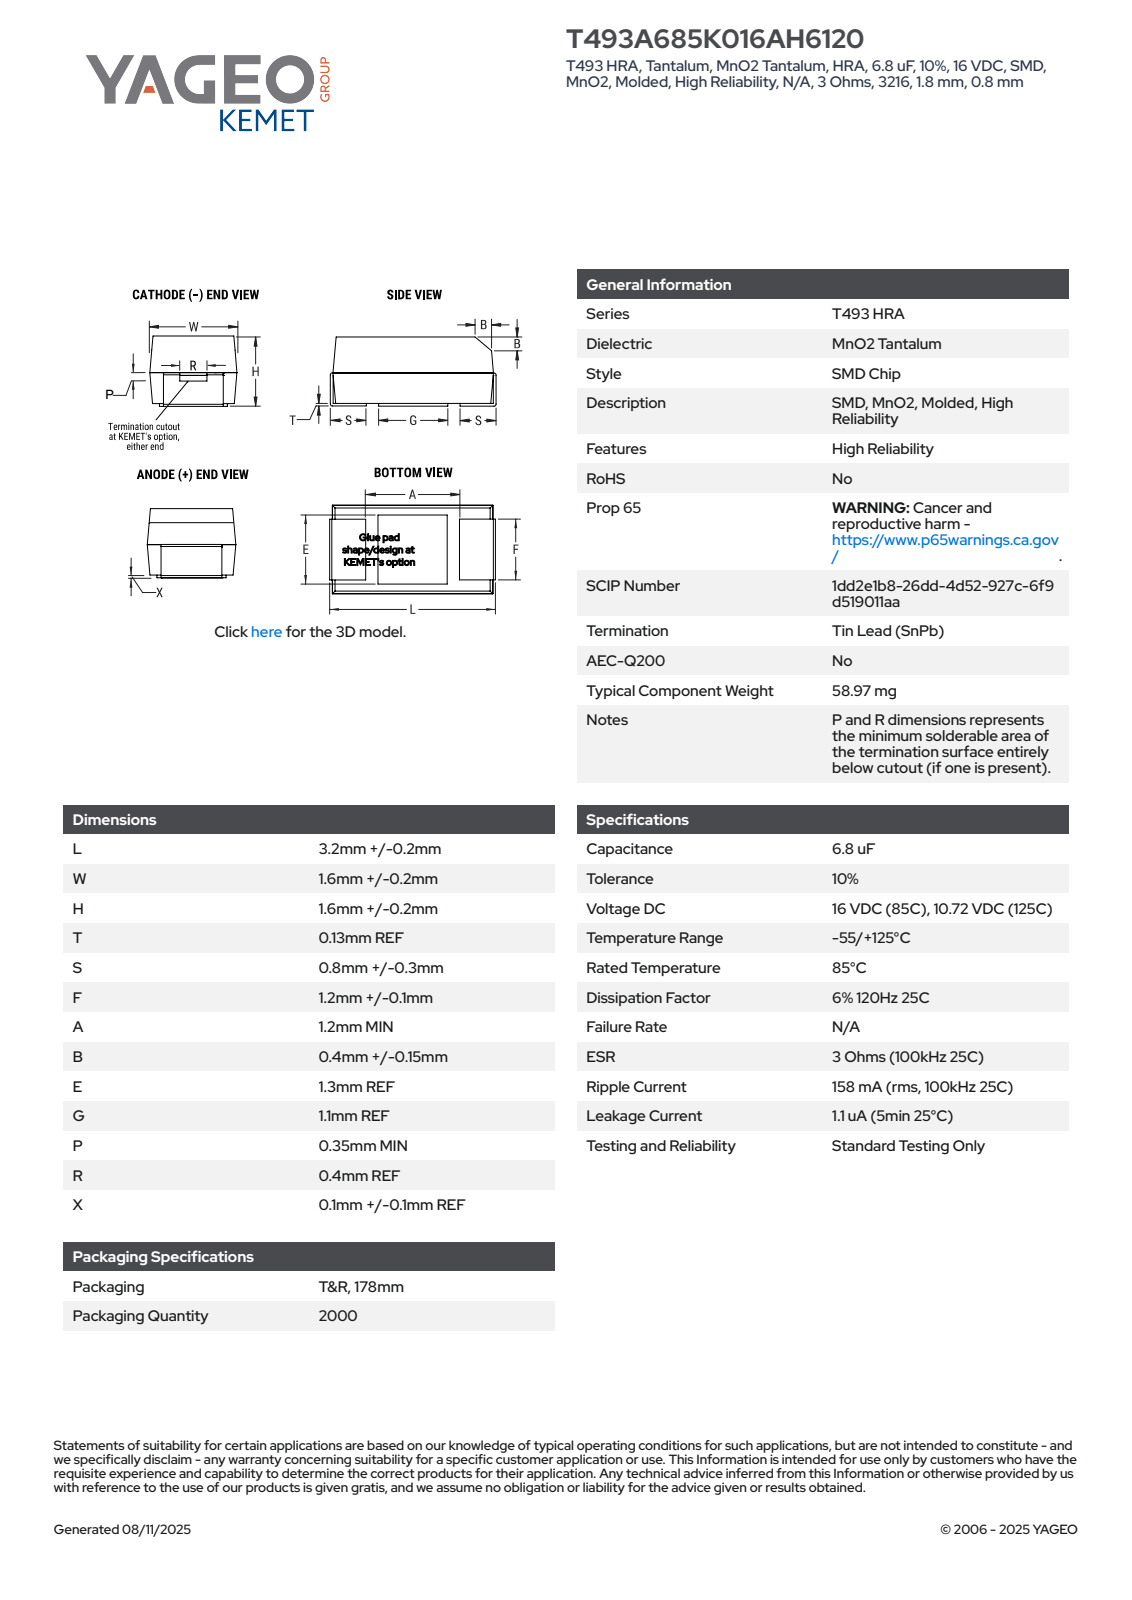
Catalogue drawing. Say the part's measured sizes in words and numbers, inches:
The part is named "CTSM_TCM2NK_3216_L3.4W1.8H1.8T0.13S0.8F1.3A1.2B0.55E1.3G1.1P0.35R0.4X0.2". Its 3-D file was written by "SolidWorks 2020 (AUTOMOTIVE_DESIGN)". It is 4 solids with 100 faces: 95 planar, 5 cylindrical and 0 other. Overall it measures 0.134 by 0.071 by 0.071 inches. Its volume is 0.001 cubic inches and its surface area 0.053 square inches. Partial cylindrical surfaces (rounded edges, fillets, slot ends): 4 of radius 0.004. The main face-to-face distances are 0.07, 0.071, 0.063, 0.066, 0.129, 0.134, 0.124, 0.045, 0.089, 0.04.
